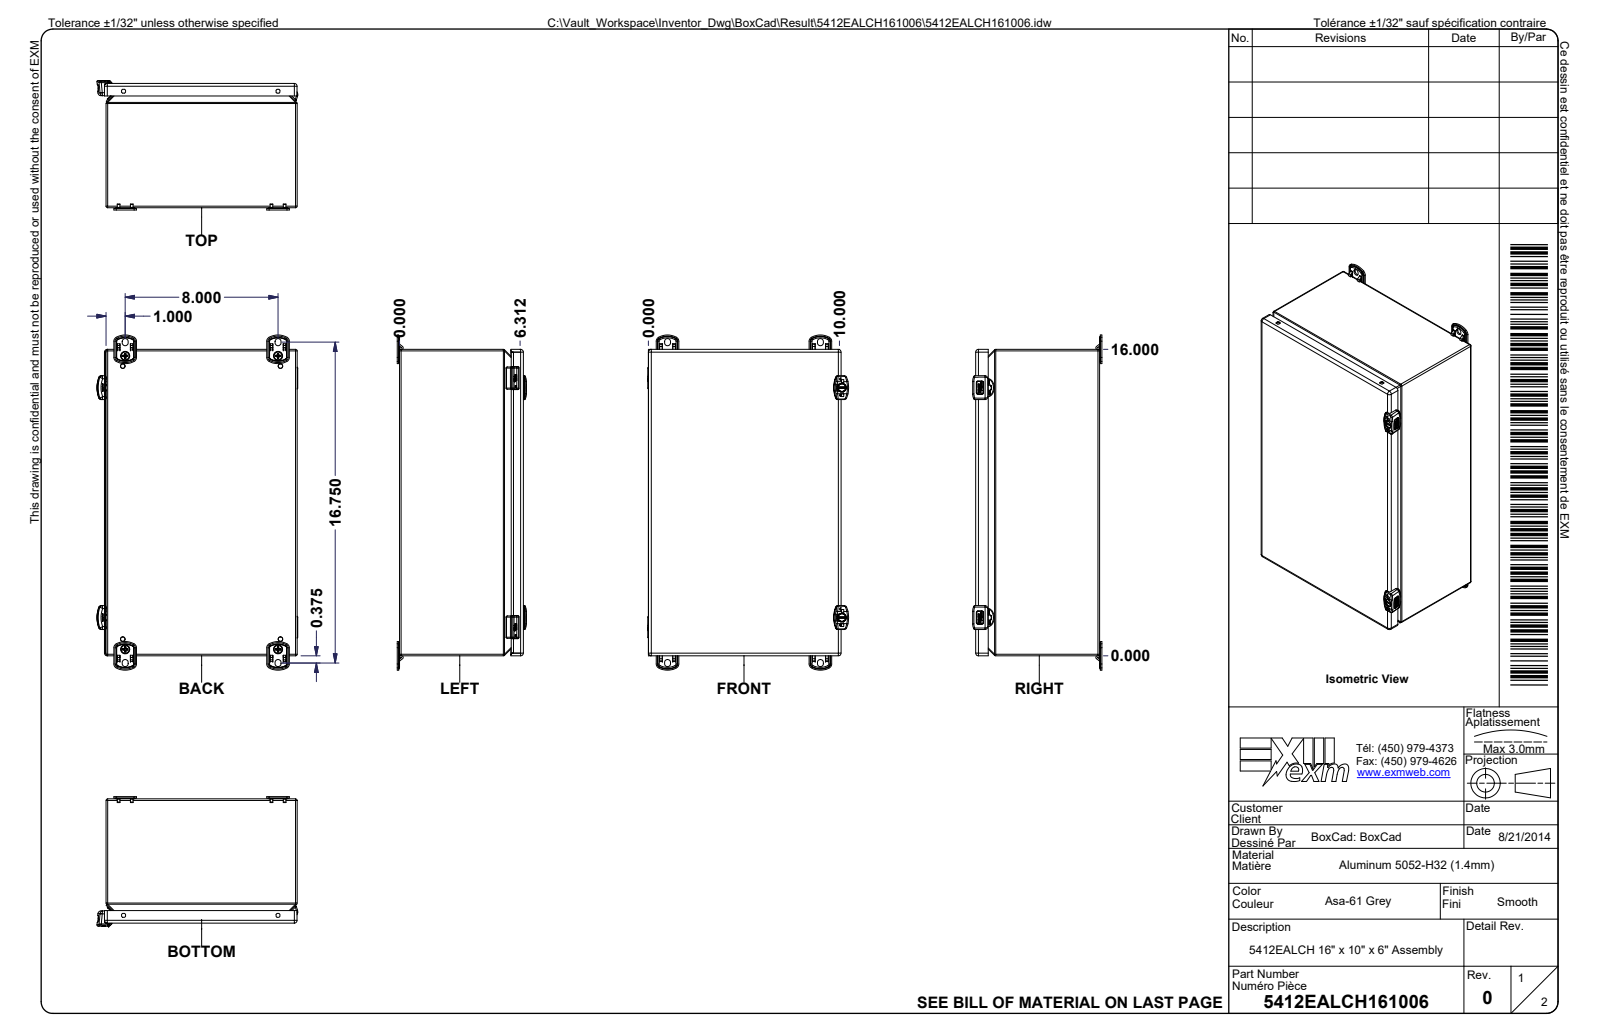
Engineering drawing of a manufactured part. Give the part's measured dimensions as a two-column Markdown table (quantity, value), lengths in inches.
| quantity | value |
| --- | --- |
| part name | 5412EALCH161006; 5412EALCH161006B; 5412EALCH161006B-P; STK-A-70469-1 (+8 more) |
| STEP written by | Autodesk Inventor 2020 (AUTOMOTIVE_DESIGN) |
| units | inches |
| bodies | 59 solids, 8409 faces (3583 planar, 2002 cylindrical, 2824 other) |
| overall size | 17.496 × 10.503 × 6.76 |
| volume | 50.19 in³ |
| surface area | 1 785 in² |
| round holes (diameter × count) | 0.165 × 4, 0.173 × 4, 0.197 × 4, 0.197 × 4, 0.236 × 4, 0.236 × 4, 0.32 × 4, 0.03 × 2, 0.175 × 2, 0.201 × 2, 0.24 × 2, 0.339 × 2 |
| round bosses / shafts (diameter × count) | 0.232 × 8, 0.5 × 4, 0.3 × 4, 0.236 × 4, 0.193 × 4, 0.197 × 3, 0.412 × 2, 0.394 × 2 |
| partial cylindrical surfaces (radius × count) | 0.02 × 257, 0.01 × 209, 0.039 × 92, 0.004 × 64, 0.008 × 60, 0.059 × 57, 0.031 × 35, 0.005 × 33 |
| main face-to-face distances | 0.053, 0.053, 9.947, 6.433, 6.38, 6.486, 6.433, 0.236, 0.304, 0.357 |
| hole center spacings | 0.546, 8.142, 14.781, 16.867, 8.25, 8.25, 13.163, 14.25 |
